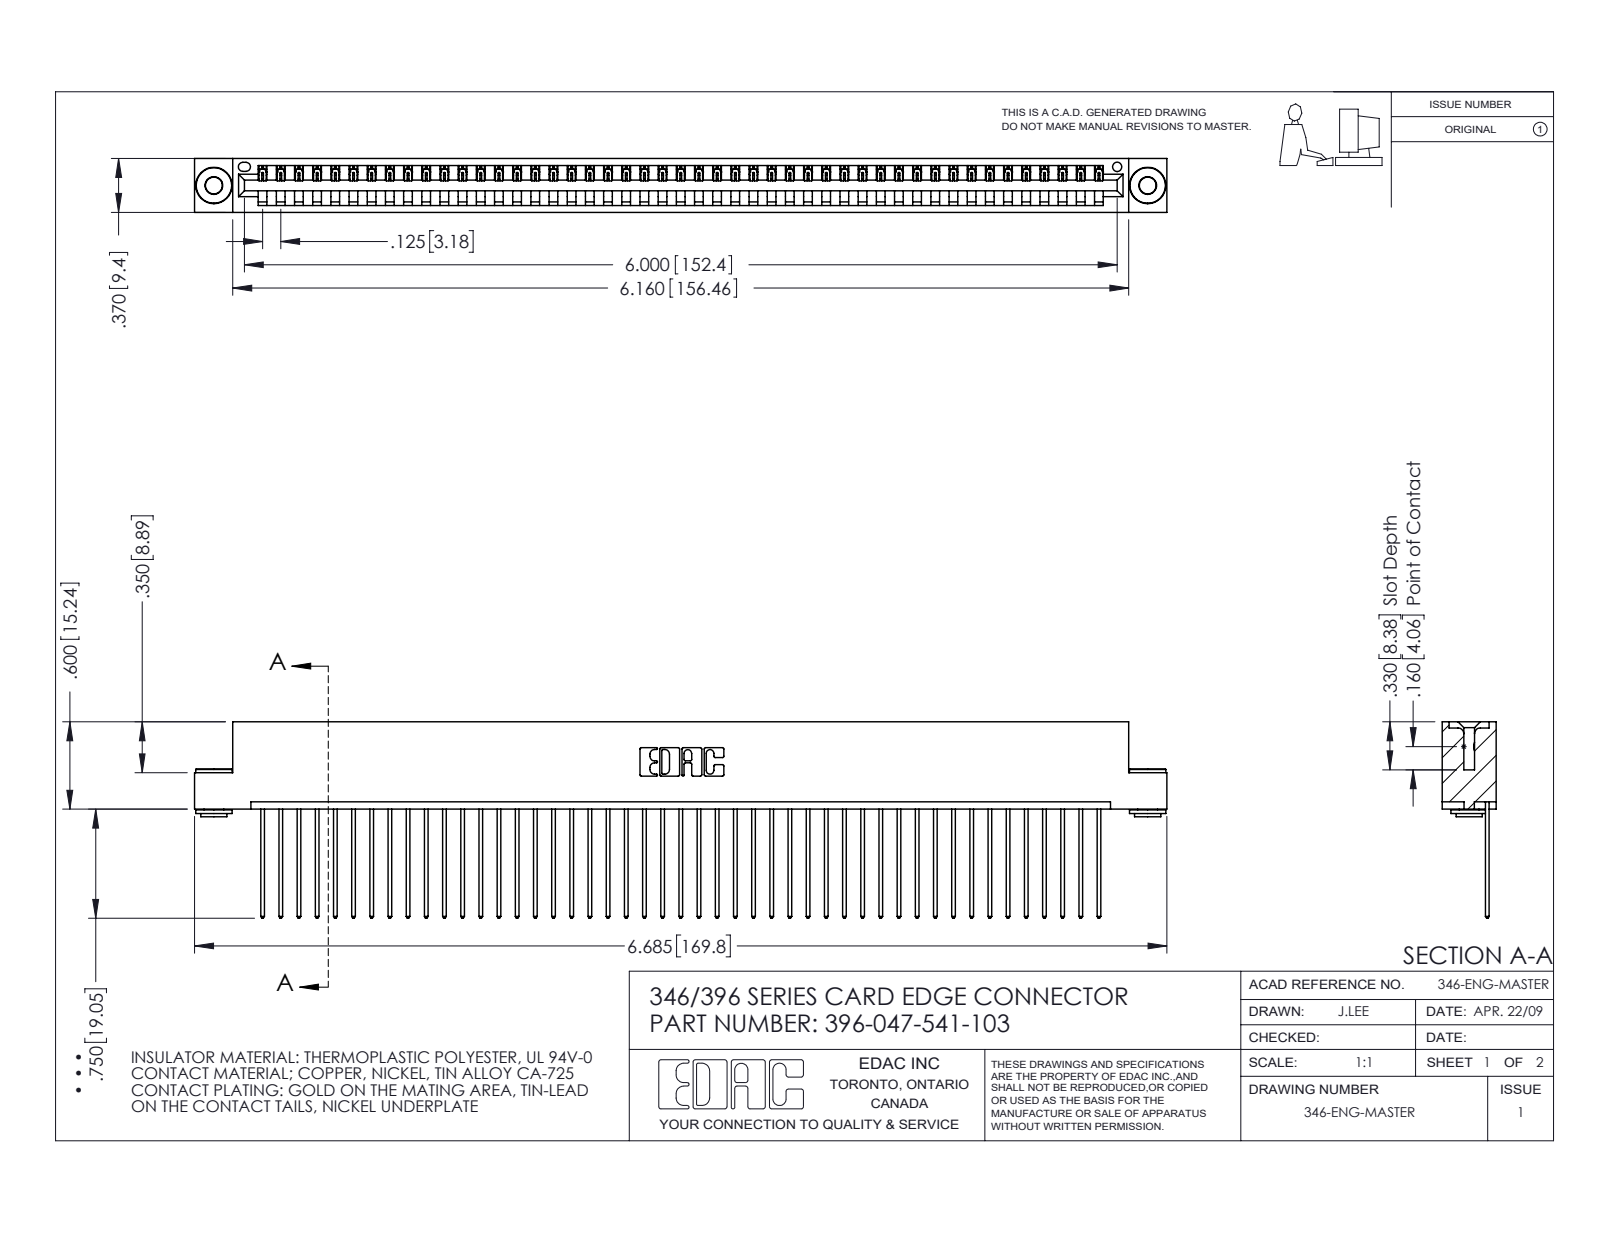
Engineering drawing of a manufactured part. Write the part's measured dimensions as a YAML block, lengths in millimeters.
part_name: "346 Part_Flush Mounting Lugs - 0.156 Dia-TH; 396-047-541-103; 345-292-001_345-293-141; 345-250-002_345-250-002-102"
step_written_by: "SolidWorks 2016 (CONFIG_CONTROL_DESIGN)"
units: millimeters
bodies: {solids: 50, faces: 2886, planar: 1966, cylindrical: 912, other: 8}
overall_size: [169.8, 34.3, 9.4]
volume: 16470
surface_area: 21770
round_holes:
  - {diameter: 2.9, count: 2}
  - {diameter: 4, count: 2}
  - {diameter: 1.6, count: 1}
round_bosses_or_shafts:
  - {diameter: 6.4, count: 2}
  - {diameter: 4.6, count: 2}
  - {diameter: 3.5, count: 2}
partial_cylinders:
  - {radius: 0.2, count: 94}
  - {radius: 0.3, count: 94}
  - {radius: 0.3, count: 22}
  - {radius: 0.2, count: 6}
  - {radius: 0.8, count: 6}
  - {radius: 0.7, count: 3}
  - {radius: 0.8, count: 2}
  - {radius: 1, count: 2}
face_to_face_distances: [1.2, 8.2, 9.4, 6.4, 0.6, 1.8, 7.6, 3.8, 5.6, 2.5]
hole_center_spacings: [6.2, 157.8, 163.1]
